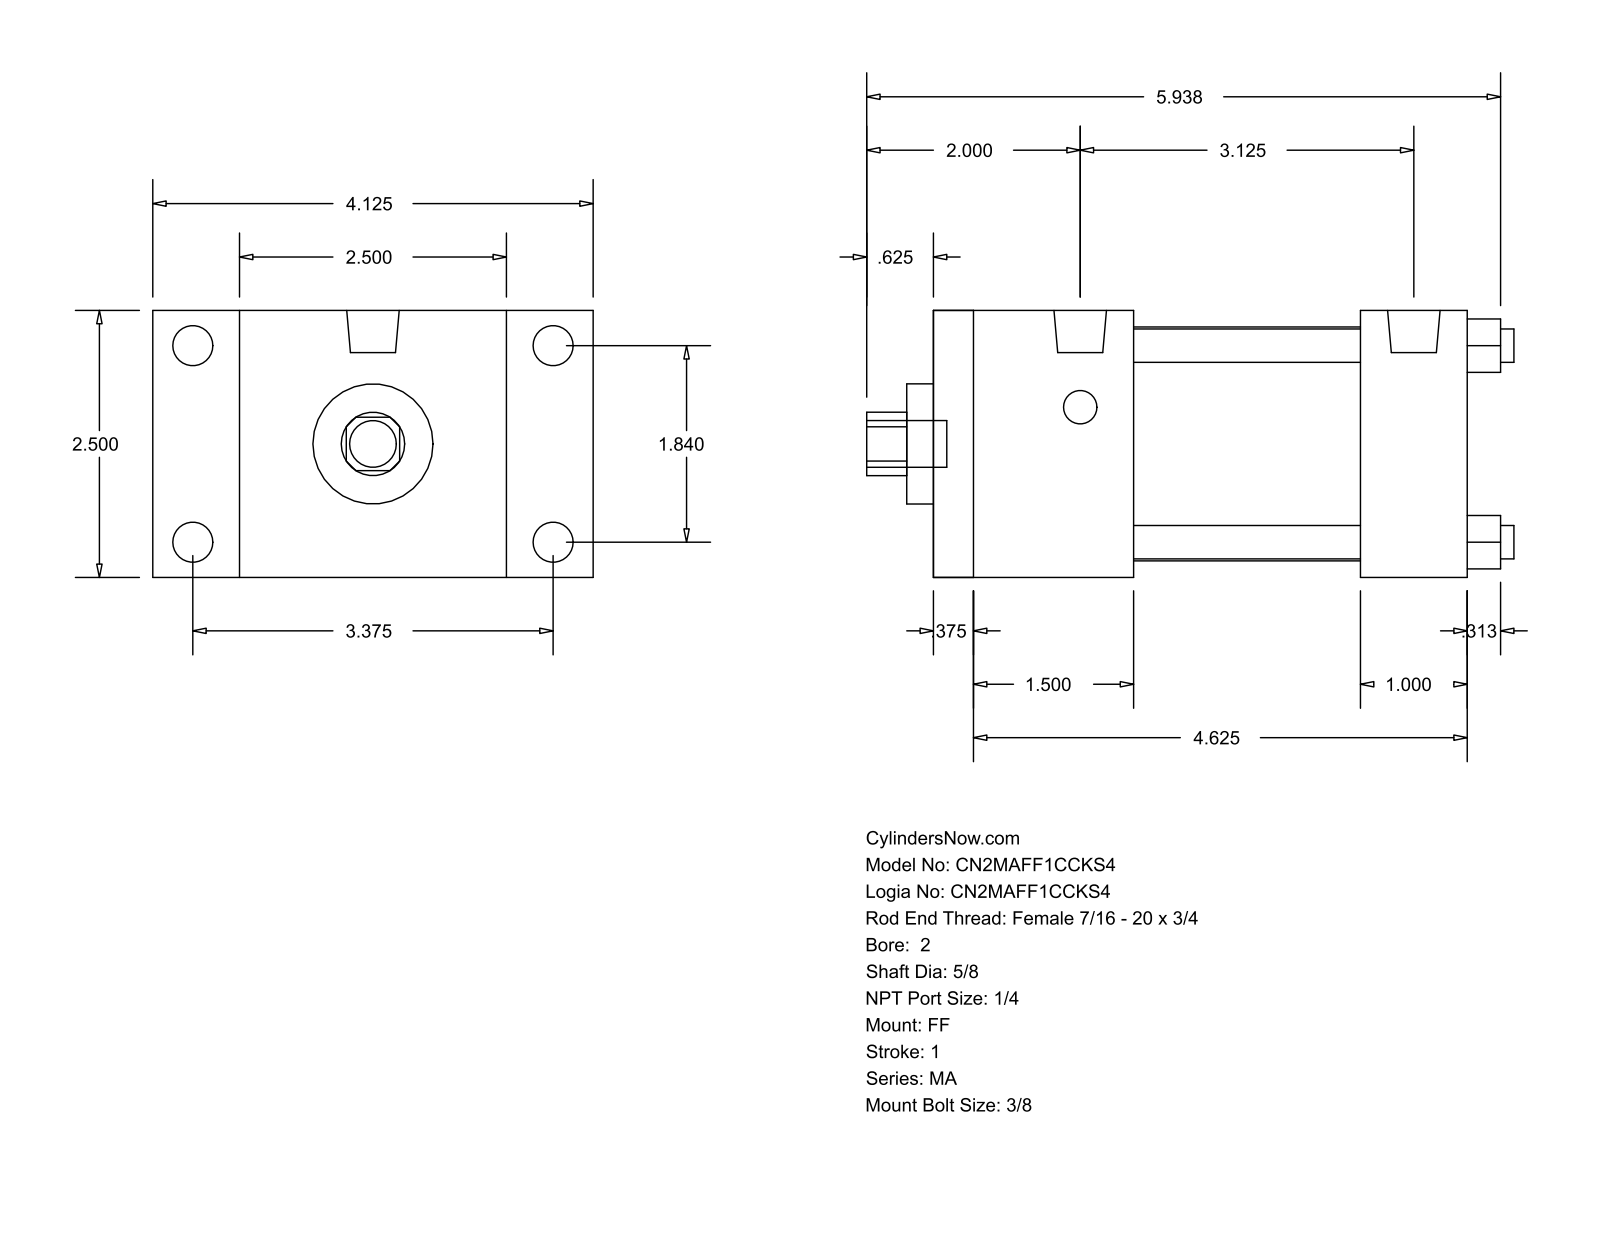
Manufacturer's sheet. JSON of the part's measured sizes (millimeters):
{"part_name": "MA_FF__0200_0.625", "step_written_by": "GSSL Pune (CONFIG_CONTROL_DESIGN)", "units": "millimeters", "bodies": {"solids": 0, "faces": 92, "planar": 64, "cylindrical": 28, "other": 0}, "overall_size": [153.99, 104.78, 63.5], "round_holes": [[7.94, 4], [15.88, 1], [28.57, 1], [55.63, 1]], "round_bosses_or_shafts": [[9.53, 4], [7.94, 4], [12.49, 2], [11.11, 1]], "partial_cylinders_radius": [[7.54, 1]], "face_to_face_distances": [63.5, 127, 9.52, 117.48, 53.97, 38.1, 47.62, 101.59, 92.07, 79.38], "hole_center_spacings": [33.05, 46.74, 66.1]}
